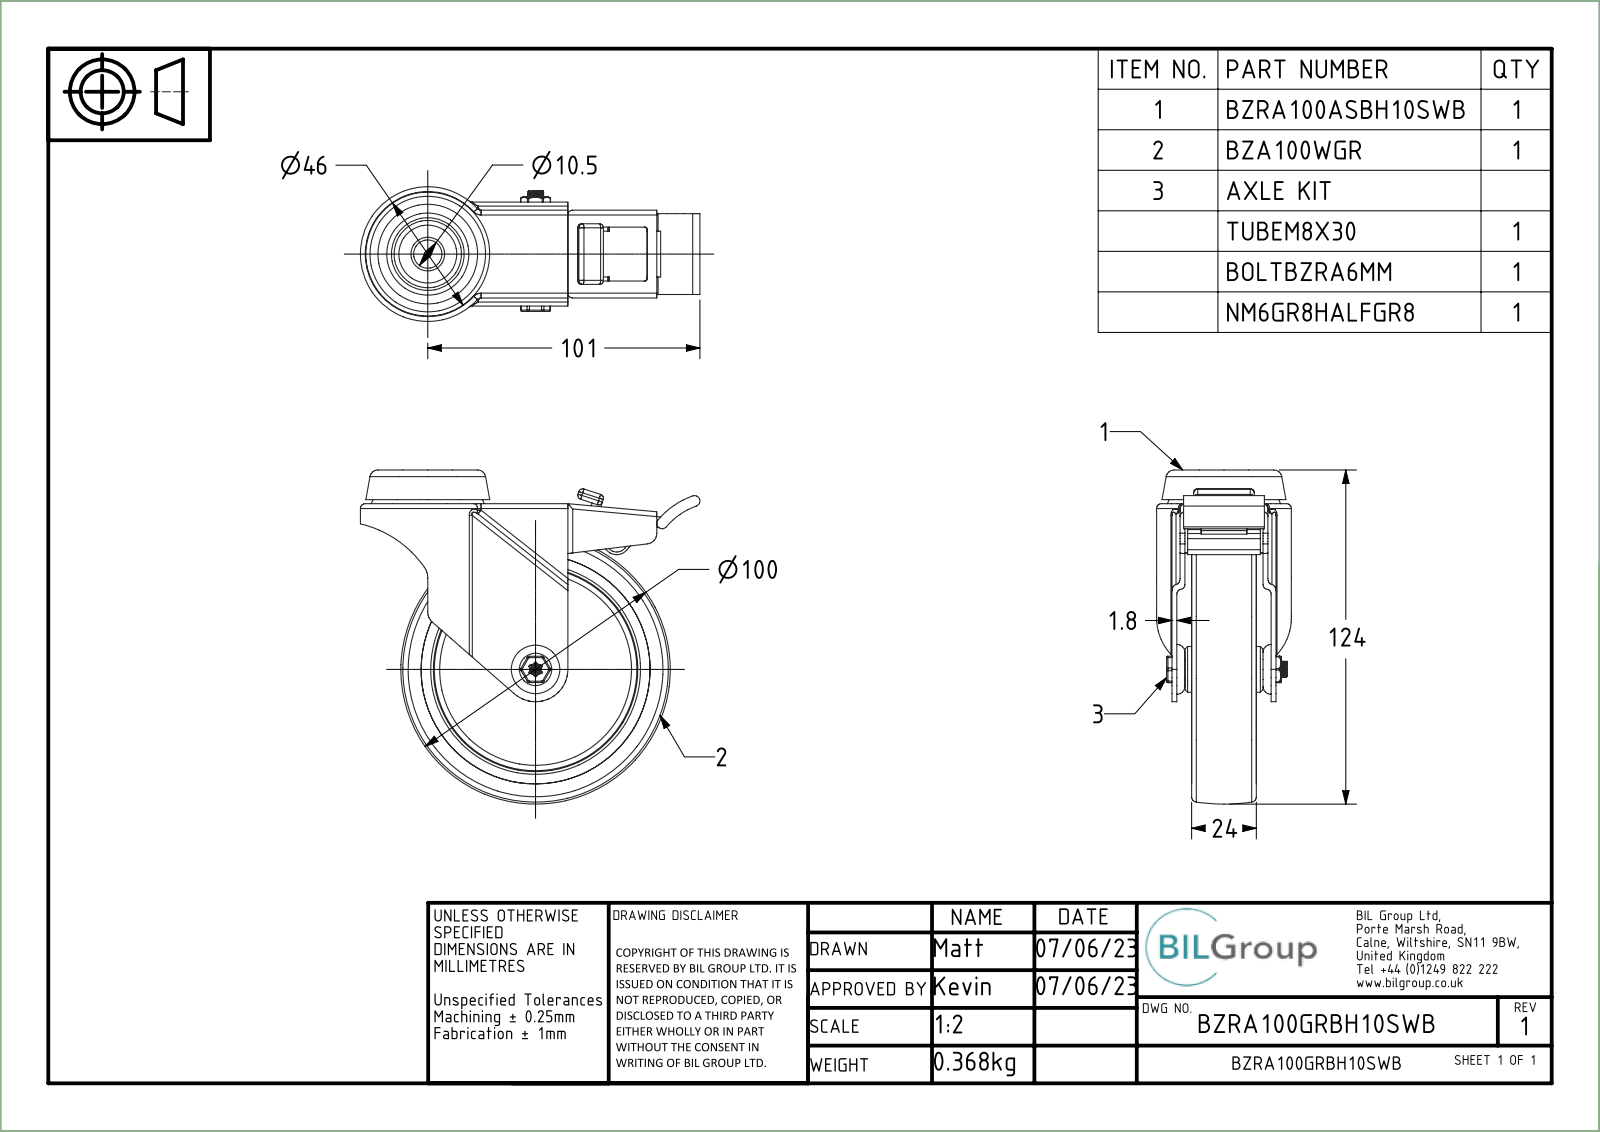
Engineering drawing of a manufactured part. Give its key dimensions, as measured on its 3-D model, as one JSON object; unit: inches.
{"part_name": "BZRA100ASBH10SWB; ZINC PLATED PRESSED STEEL HEAD; ZINC PLATED PRESSED STEEL FORKS; ZINC PLATED PRESSED STEEL BRAKE (+8 more)", "step_written_by": "Spatial InterOp 3D (CONFIG_CONTROL_DESIGN)", "units": "inches", "bodies": {"solids": 10, "faces": 630, "planar": 200, "cylindrical": 254, "other": 176}, "overall_size": [4.961, 4.882, 1.969], "volume_in3": 9.293, "surface_area_in2": 131.9, "round_holes": [[0.236, 1], [0.248, 1], [0.252, 1], [0.327, 1], [0.331, 1], [0.413, 1], [0.416, 1], [1.181, 1], [3.346, 1]], "round_bosses_or_shafts": [[1.535, 1], [0.709, 1], [0.669, 1], [0.581, 1], [0.315, 1], [0.313, 1], [0.197, 1]], "partial_cylinders_radius": [[0.071, 27], [0.039, 22], [0.02, 13], [0.059, 12], [0.016, 6], [0.035, 4], [0.079, 4], [0.197, 2]], "face_to_face_distances": [0.071, 1.331, 0.354, 0.591, 0.118, 0.236, 0.453, 0.098, 0.189, 0.689]}
